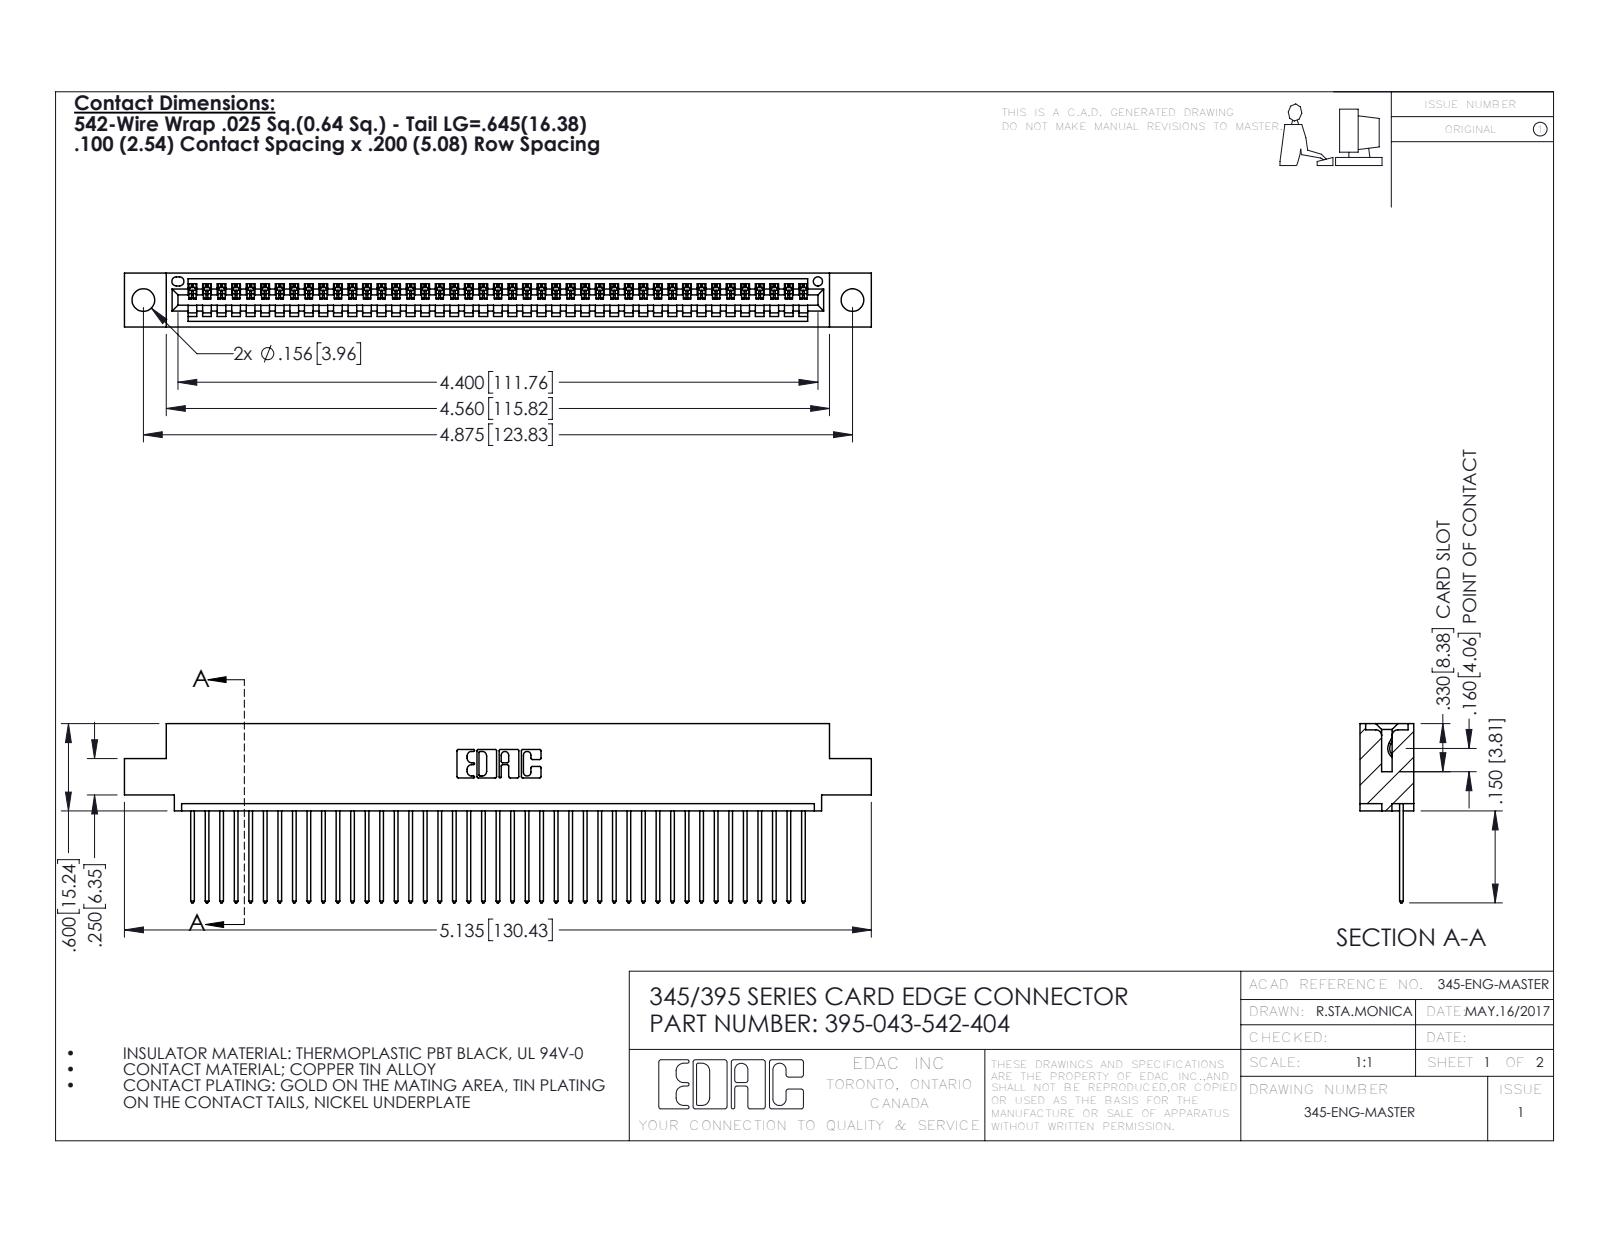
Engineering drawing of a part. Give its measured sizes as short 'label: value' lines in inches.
name: 345-292-001_345-293-142; 345 Part_0.110 Offset - 0.156 Dia-TH; 395-043-542-404
written by: SolidWorks 2016 (CONFIG_CONTROL_DESIGN)
unit: in
bodies: 44 solids, 2624 faces (1804 planar, 820 cylindrical, 0 other)
size: 5.135 × 1.232 × 0.37
volume: 0.752 in³; area: 26.19 in²
holes: 2× ⌀0.156, 1× ⌀0.064
rounds: 86× R0.006, 86× R0.01, 22× R0.01, 6× R0.007, 6× R0.031, 3× R0.026, 2× R0.031, 2× R0.04
face distances: 0.072, 0.298, 0.37, 0.098, 0.272, 0.025, 0.2, 0.225, 0.149, 0.072
hole spacings: 0.27, 4.639, 4.875
